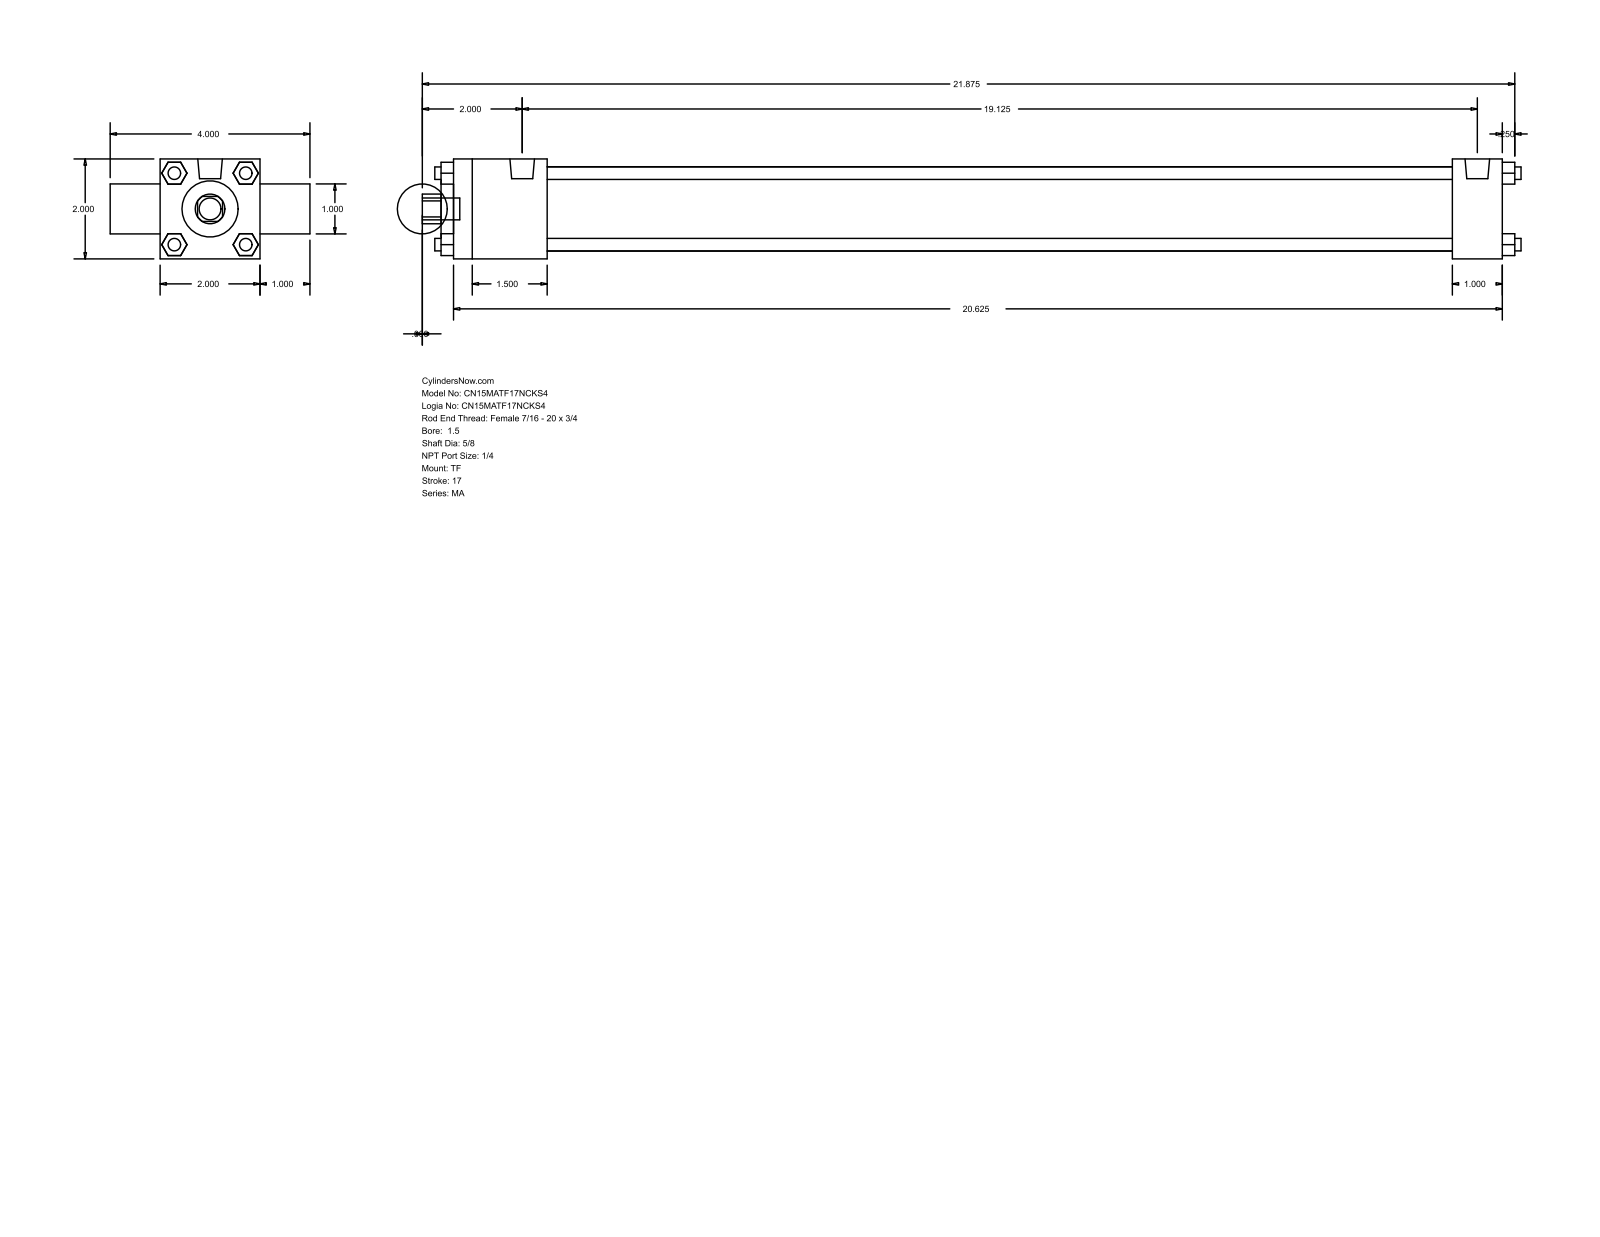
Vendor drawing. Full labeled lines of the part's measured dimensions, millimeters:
Part name (STEP PRODUCT): MA_TF__0150_0.625
STEP written by: GSSL Pune (CONFIG_CONTROL_DESIGN)
Units: millimetres
Bodies: 0 solids, 120 faces (92 planar, 28 cylindrical, 0 other)
Overall size (bounding box): 558.8 × 101.6 × 50.8
Round holes (diameter × count): ⌀15.88 ×1, ⌀25.4 ×1, ⌀28.57 ×1, ⌀42.93 ×1
Round bosses / shafts (diameter × count): ⌀6.35 ×4, ⌀7.94 ×3, ⌀12.49 ×2, ⌀11.11 ×1
Partial cylindrical surfaces — rounded edges, fillets, slot ends (radius × count): R7.54 ×1
Main face-to-face distances: 50.8, 533.39, 6.35, 539.74, 25.4, 76.2, 47.62, 508, 460.38, 485.77
